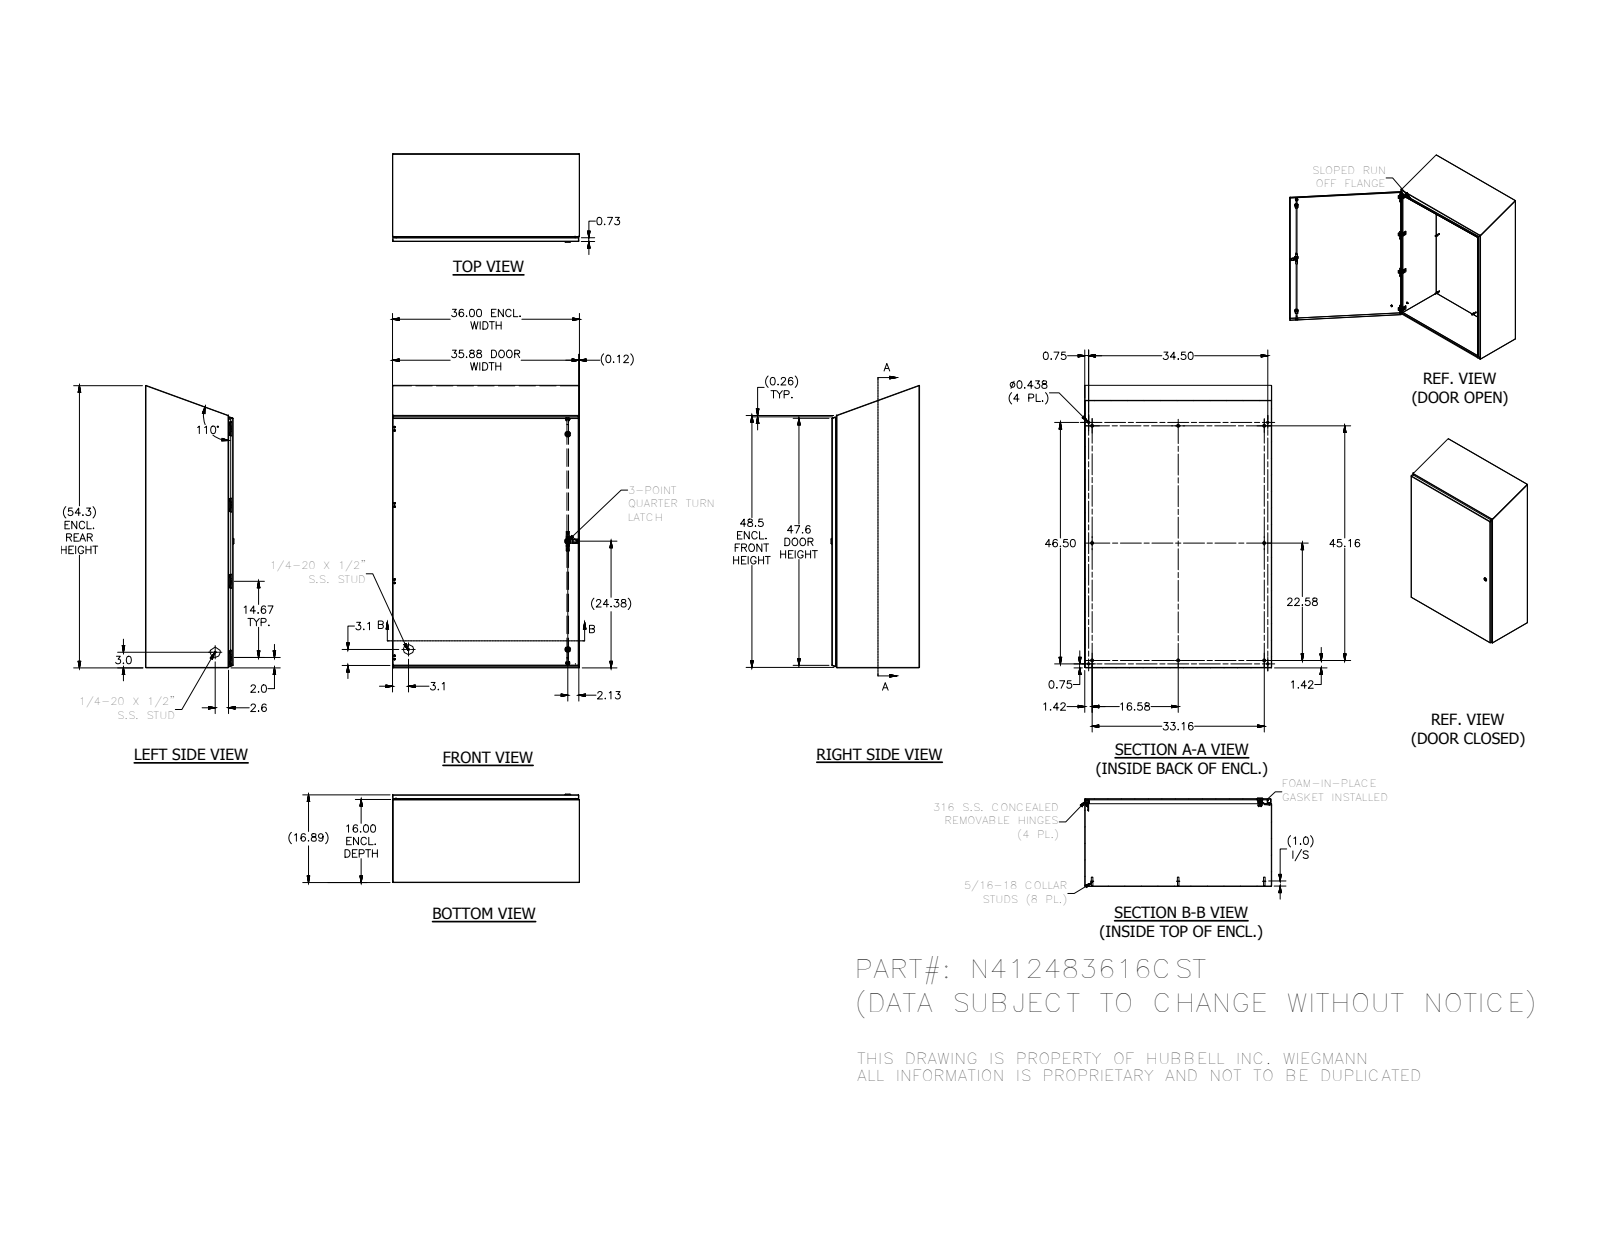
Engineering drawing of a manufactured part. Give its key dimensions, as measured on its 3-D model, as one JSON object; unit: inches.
{"part_name": "N412_CST-assm3pcblr; N412483616CSTBLR; HFW3161; HFW328176 (+8 more)", "step_written_by": "Autodesk Inventor 2012 (AUTOMOTIVE_DESIGN)", "units": "inches", "bodies": {"solids": 79, "faces": 2617, "planar": 954, "cylindrical": 979, "other": 684}, "overall_size": [54.377, 36, 17.044], "volume_in3": 512.9, "surface_area_in2": 13855, "round_holes": [[0.093, 8], [0.152, 8], [0.167, 8], [0.172, 8], [0.187, 8], [0.156, 5], [0.165, 4], [0.197, 4], [0.437, 4], [0.106, 2], [0.16, 2], [0.169, 2]], "round_bosses_or_shafts": [[0.25, 18], [0.563, 8], [0.36, 8], [0.32, 8], [0.3, 8], [0.275, 8], [0.256, 8], [0.164, 8]], "partial_cylinders_radius": [[0.05, 50], [0.031, 36], [0.016, 34], [0.125, 32], [0.012, 31], [0.02, 20], [0.105, 18], [0.032, 16]], "face_to_face_distances": [0.074, 16.813, 16.739, 16.887, 35.926, 35.852, 36, 15.926, 0.887, 0.813], "hole_center_spacings": [14.667, 29.333, 14.667, 44, 0.5, 0.656, 1.307, 14.675]}
